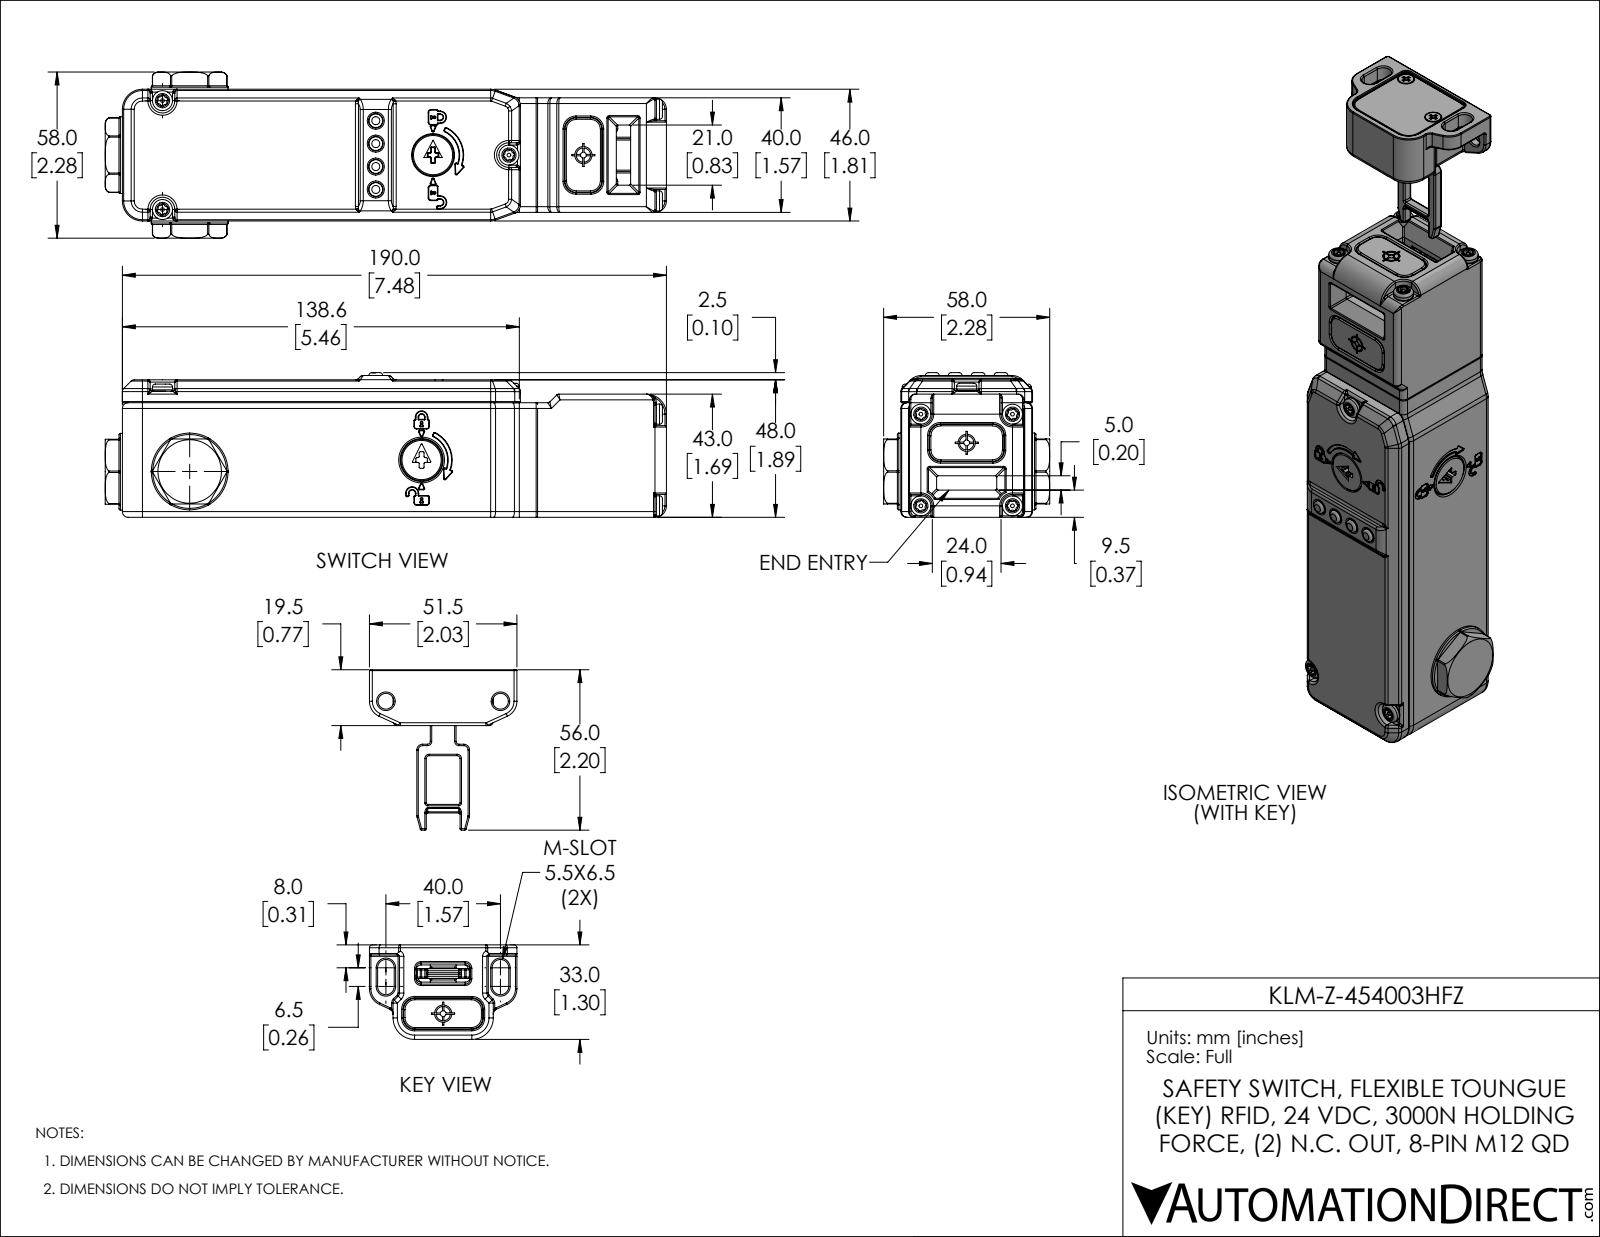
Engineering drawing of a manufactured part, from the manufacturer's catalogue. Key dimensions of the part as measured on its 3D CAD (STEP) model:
Part name (STEP PRODUCT): 454-KLM-Z-HFZ
STEP written by: SolidWorks 2019 (AUTOMOTIVE_DESIGN)
Units: inches
Bodies: 25 solids, 3821 faces (1072 planar, 1495 cylindrical, 1254 other)
Overall size (bounding box): 10.118 × 2.283 × 1.988
Volume: 20.28 in³ · Surface area: 154.6 in²
Round holes (diameter × count): ⌀0.157 ×9, ⌀0.098 ×6, ⌀0.236 ×6, ⌀0.177 ×4, ⌀0.197 ×4, ⌀0.146 ×3, ⌀0.165 ×3, ⌀0.138 ×2, ⌀0.217 ×2, ⌀0.591 ×2, ⌀0.079 ×1, ⌀0.083 ×1
Round bosses / shafts (diameter × count): ⌀0.138 ×11, ⌀0.276 ×7, ⌀0.051 ×7, ⌀0.197 ×5, ⌀0.189 ×4, ⌀1.055 ×2, ⌀0.764 ×2, ⌀0.709 ×2
Partial cylindrical surfaces — rounded edges, fillets, slot ends (radius × count): R0.02 ×507, R0.012 ×139, R0.039 ×116, R0.008 ×97, R0.079 ×61, R0.059 ×35, R0.157 ×35, R0.031 ×34
Main face-to-face distances: 1.575, 0.118, 1.811, 1.693, 0.315, 1.89, 0.098, 0.079, 1.791, 0.217
Hole centre spacings: 0.319, 0.481, 0.63, 0.748, 1.043, 1.043, 1.081, 1.26
